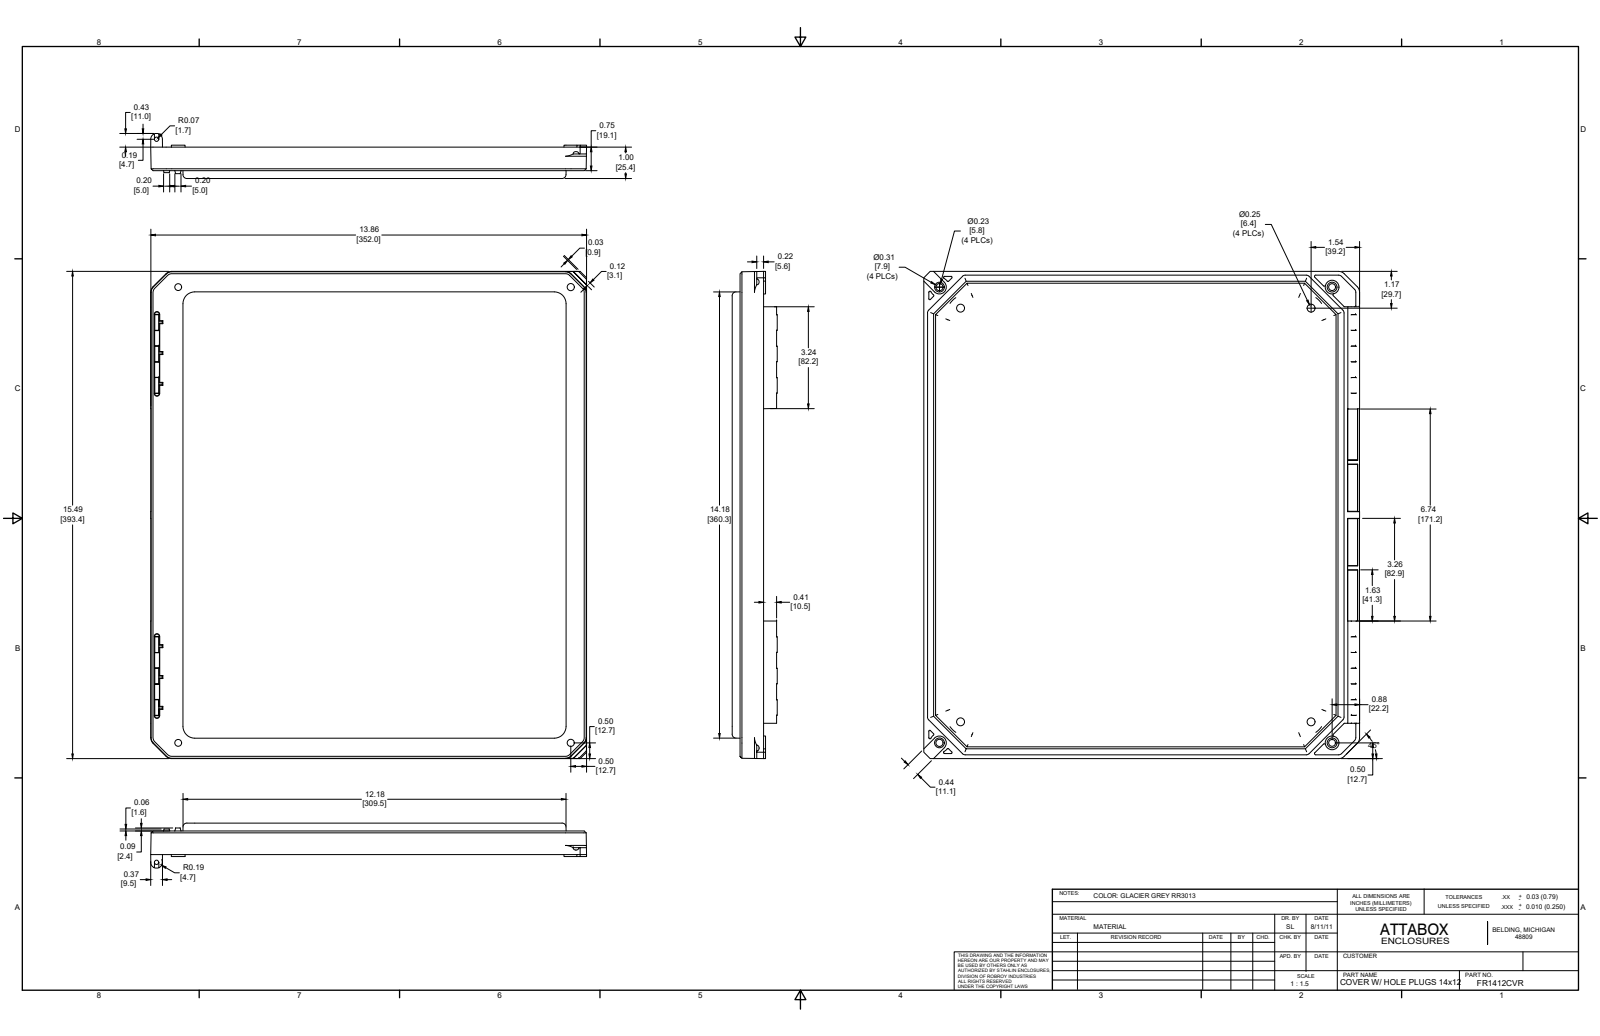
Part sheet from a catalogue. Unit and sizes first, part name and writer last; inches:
Units: inches
Overall size (bounding box): 15.489 × 13.864 × 1.434
Round holes (diameter × count): ⌀0.253 ×4, ⌀0.219 ×2, ⌀0.227 ×2, ⌀0.313 ×2, ⌀0.137 ×1
Round bosses / shafts (diameter × count): ⌀0.435 ×2
Partial cylindrical surfaces — rounded edges, fillets, slot ends (radius × count): R0.03 ×27, R0.01 ×18, R0.096 ×16, R0.063 ×13, R0.125 ×12, R0.062 ×11, R0.04 ×10, R0.06 ×9
Main face-to-face distances: 0.125, 0.125, 0.25, 0.375, 0.75, 0.25, 0.875, 1, 0.625, 0.375
Hole centre spacings: 13.836, 0.946, 0.947, 11.15, 11.838, 11.839, 12.489, 13.15
Volume: 43.09 in³ · Surface area: 565.3 in²
Bodies: 1 solid, 619 faces (259 planar, 200 cylindrical, 160 other)
Part name (STEP PRODUCT): FR1412CVR
STEP written by: SolidWorks 2019 (AUTOMOTIVE_DESIGN)
